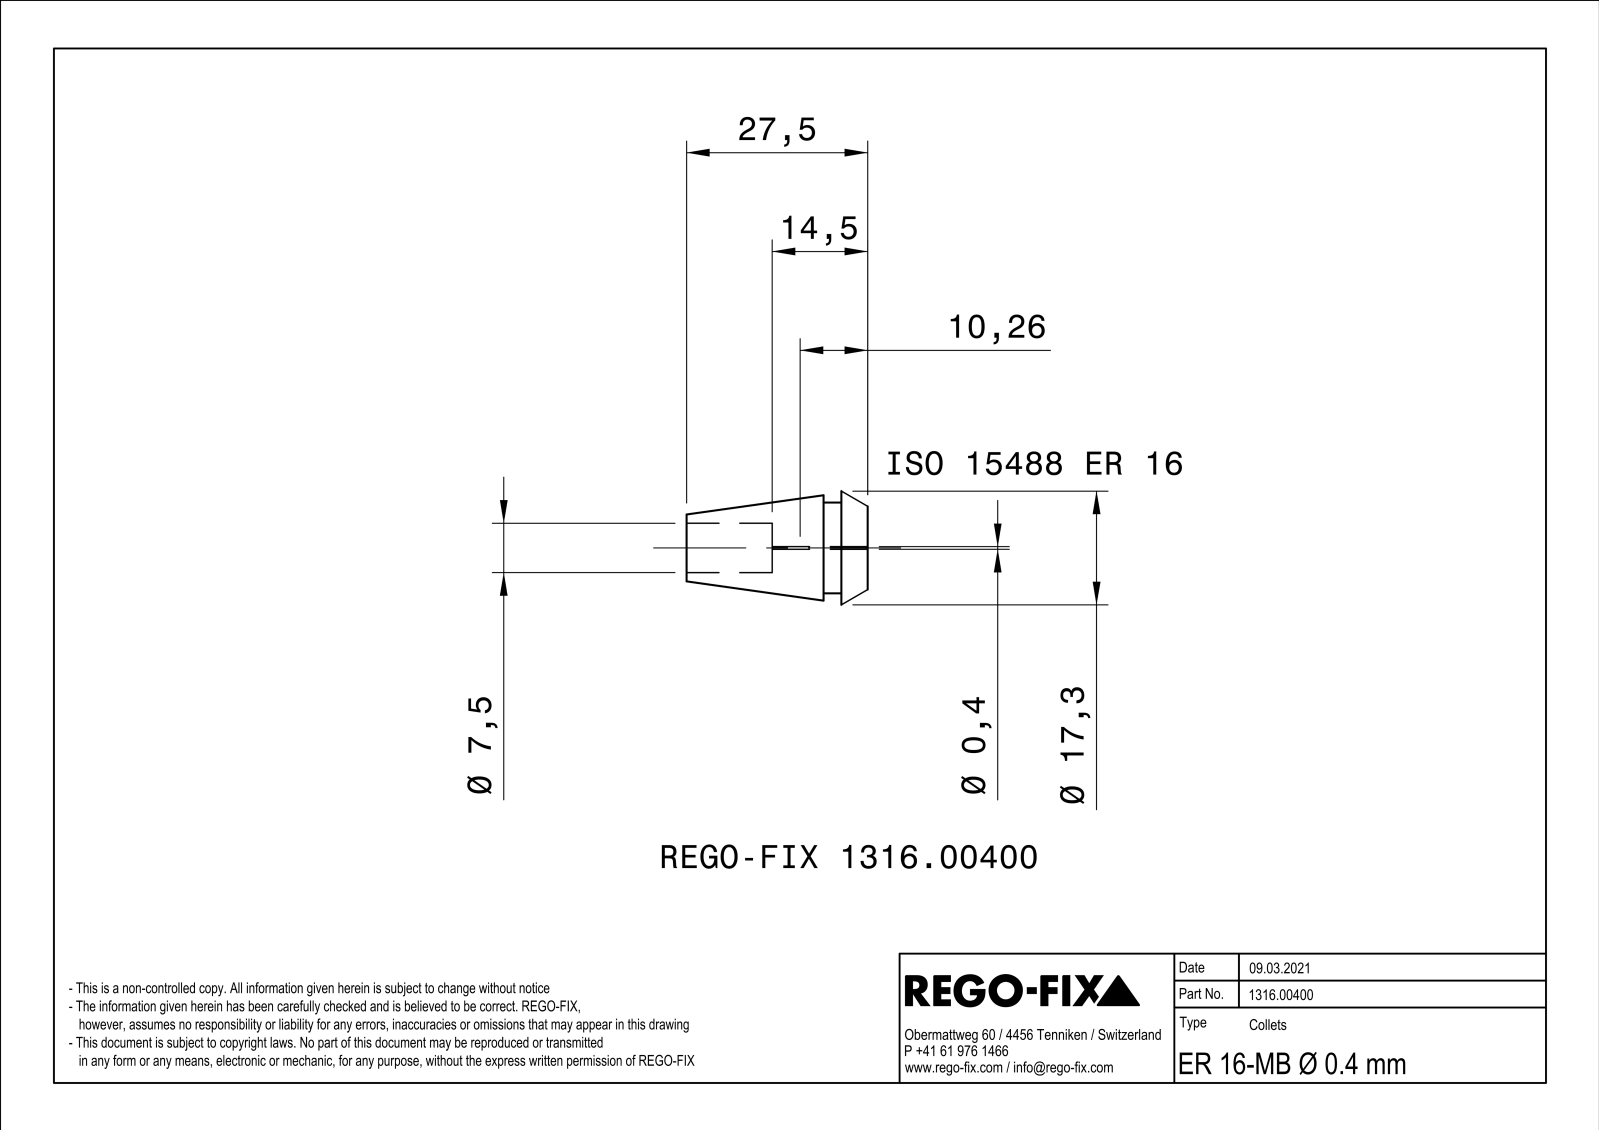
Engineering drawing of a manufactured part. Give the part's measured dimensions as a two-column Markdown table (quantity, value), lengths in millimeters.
| quantity | value |
| --- | --- |
| part name | NOCUT |
| STEP written by | SIEMENS PLM Software Solid Edge ST10 (AUTOMOTIVE_DESIGN) |
| units | millimeters |
| bodies | 1 solid, 69 faces (29 planar, 13 cylindrical, 27 other) |
| overall size | 27.5 × 17.25 × 17.25 |
| volume | 2 967 mm³ |
| surface area | 2 760 mm² |
| round holes (diameter × count) | 2 × 3, 7.5 × 1 |
| round bosses / shafts (diameter × count) | 13.8 × 1 |
| partial cylindrical surfaces (radius × count) | 0.2 × 1 |
| main face-to-face distances | 0.8, 0.51, 4, 6.7, 2.7, 27.5, 23.5, 20.8, 14.5, 10.5 |
| hole center spacings | 2.1, 3.64 |
